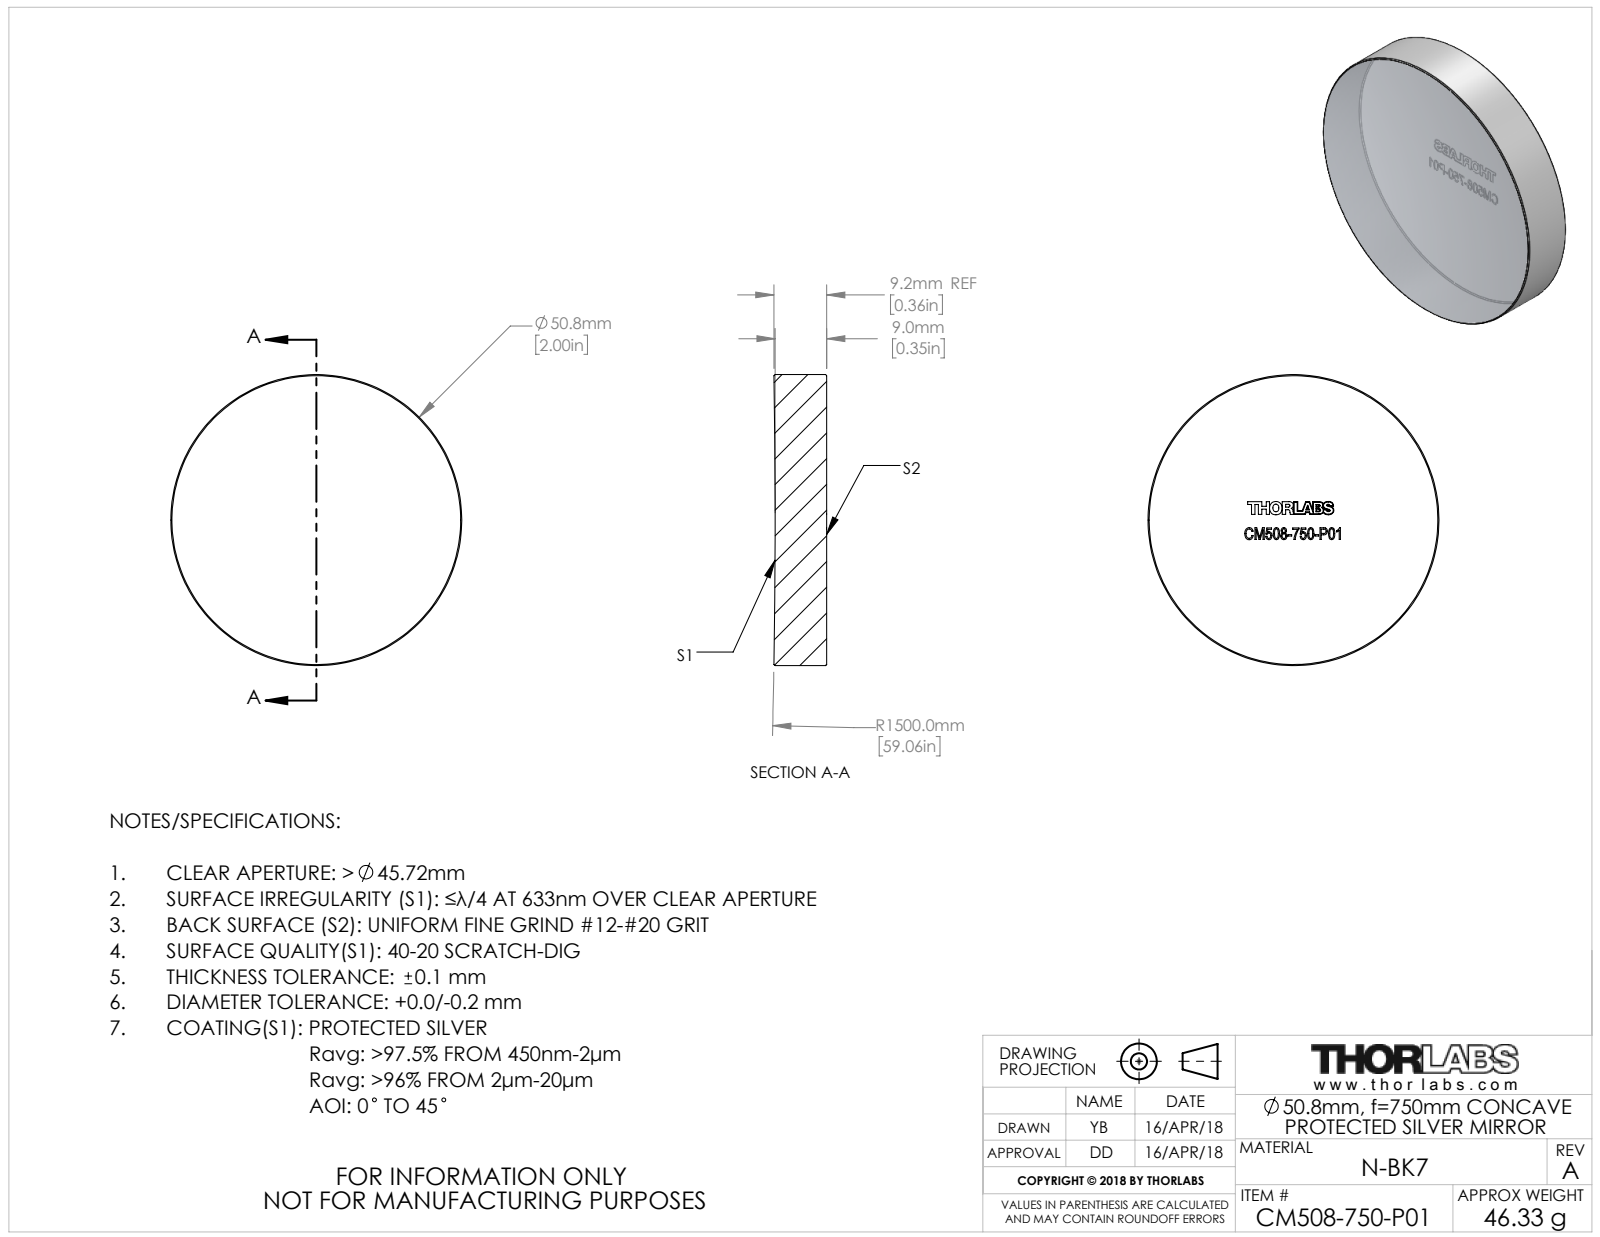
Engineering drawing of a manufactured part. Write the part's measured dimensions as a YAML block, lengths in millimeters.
part_name: "TTN153332-E0W"
step_written_by: "SolidWorks 2018 (CONFIG_CONTROL_DESIGN)"
units: millimeters
bodies: {solids: 1, faces: 43, planar: 35, cylindrical: 2, other: 6}
overall_size: [50.8, 50.8, 9.21]
volume: 18453
surface_area: 5487
round_bosses_or_shafts:
  - {diameter: 50.8, count: 1}
